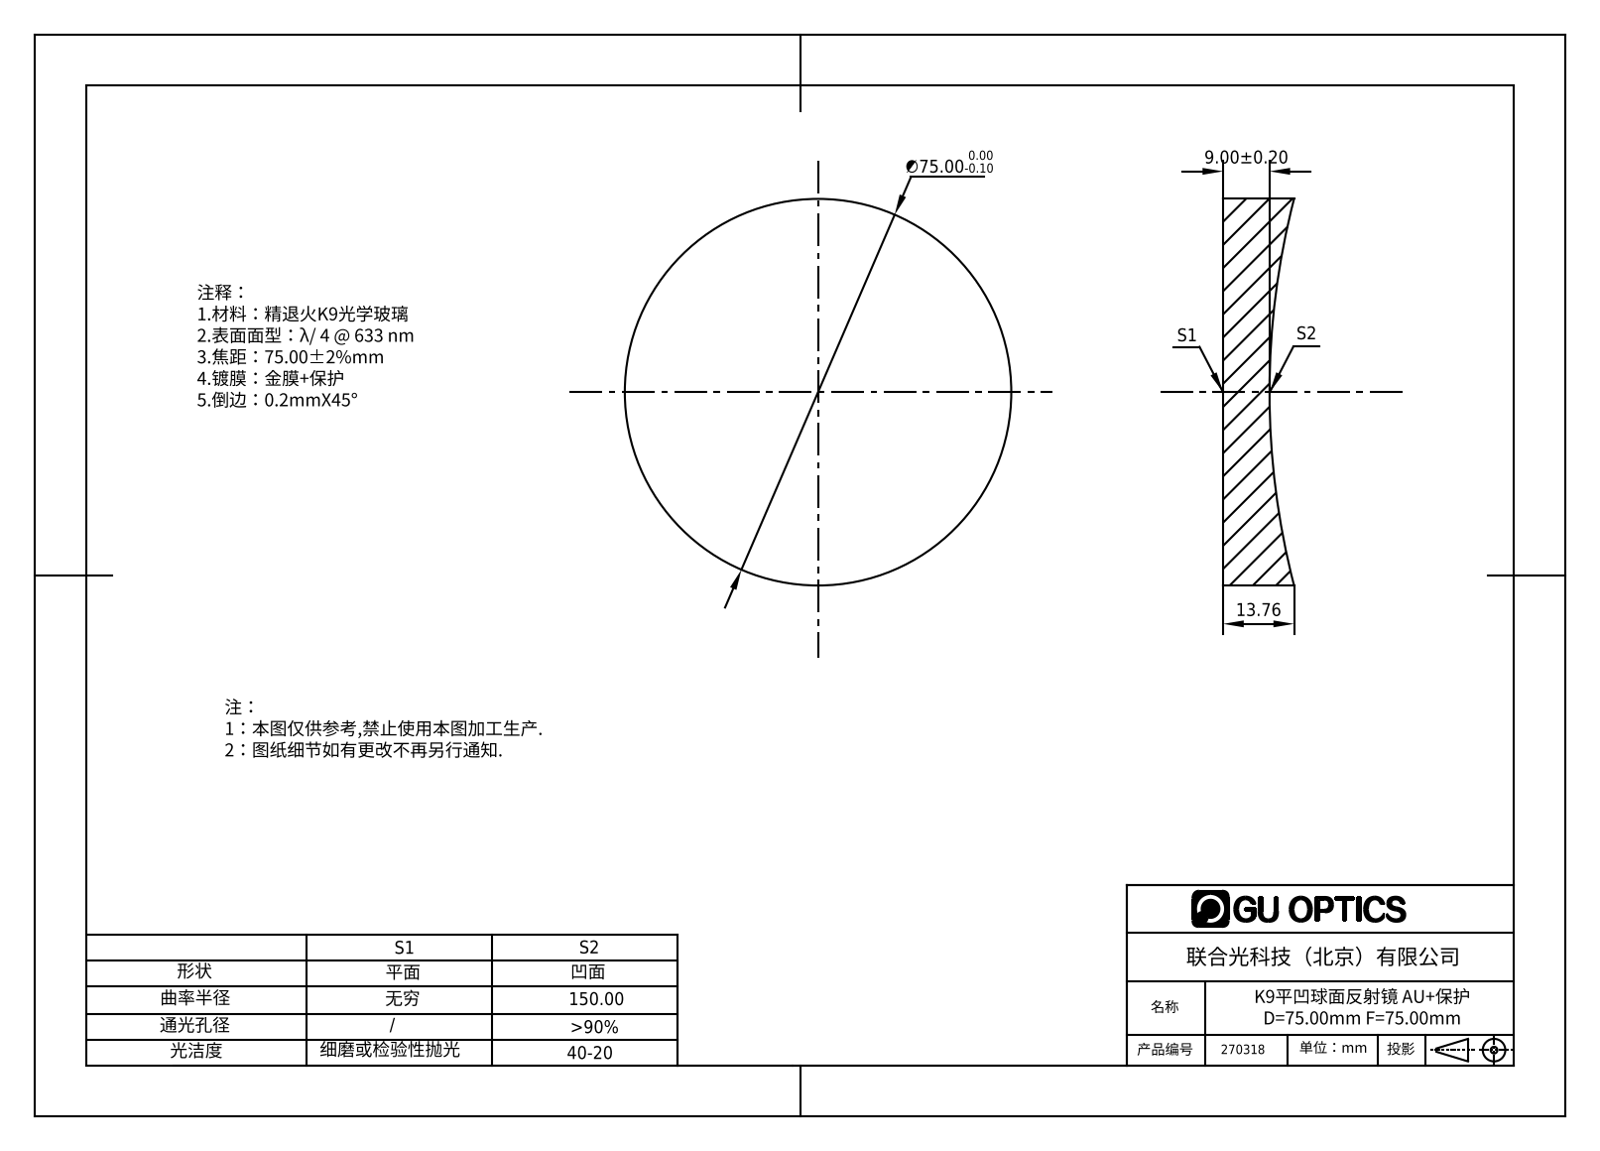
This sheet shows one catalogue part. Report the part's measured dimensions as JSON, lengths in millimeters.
{"part_name": "270058", "step_written_by": "SolidWorks 2016 (AUTOMOTIVE_DESIGN)", "units": "millimeters", "bodies": {"solids": 1, "faces": 5, "planar": 1, "cylindrical": 2, "other": 2}, "overall_size": [75, 75, 13.76], "volume_mm3": 50226, "surface_area_mm2": 12150, "round_bosses_or_shafts": [[75, 1]]}
